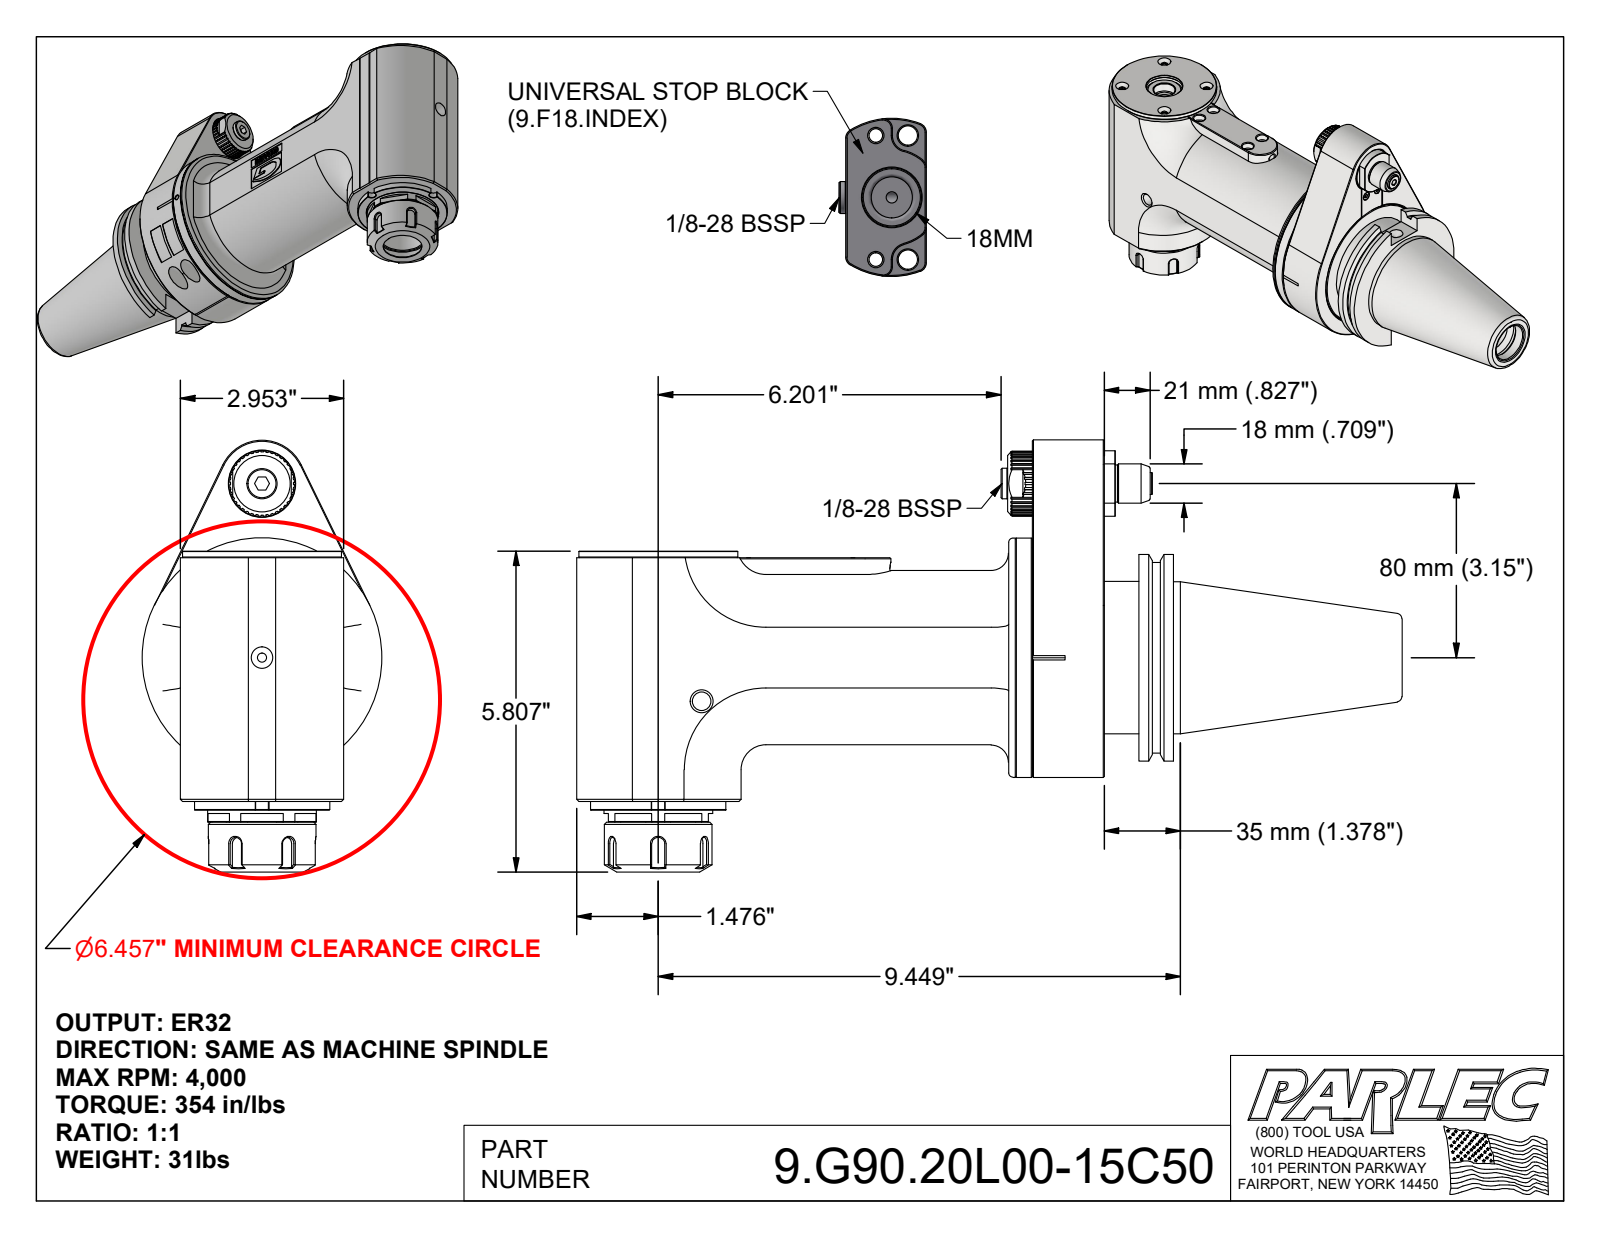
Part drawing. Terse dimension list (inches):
name: 9.G90.20L00-15C50; 9_GA2_458_1 (Classic, Type 2, Cat50, 80mm); 9_G90_20L00
written by: Autodesk Inventor 2022 (AUTOMOTIVE_DESIGN)
unit: in
bodies: 4 solids, 936 faces (471 planar, 203 cylindrical, 262 other)
size: 14.933 × 7.815 × 4.331
volume: 126.5 in³; area: 343.6 in²
holes: 13× ⌀0.197, 9× ⌀0.13, 8× ⌀0.177, 4× ⌀0.315, 4× ⌀0.335, 2× ⌀0.157, 2× ⌀0.165, 2× ⌀0.236, 2× ⌀0.276, 2× ⌀0.413, 2× ⌀0.433, 1× ⌀0.551
bosses: 2× ⌀0.394, 1× ⌀4.331, 1× ⌀4.016, 1× ⌀3.875, 1× ⌀3.593, 1× ⌀3.524, 1× ⌀3.15, 1× ⌀2.874
rounds: 7× R0.118, 2× R0.085, 2× R0.315, 2× R0.469, 2× R0.472, 2× R1.575, 1× R0.079, 1× R0.098
face distances: 1.299, 0.315, 0.984, 0.626, 2.953, 0.118, 0.941, 1.925, 0.197, 2.551
hole spacings: 1.87, 0.968, 1.161, 1.643, 2.645, 3.239, 3.613, 3.74
